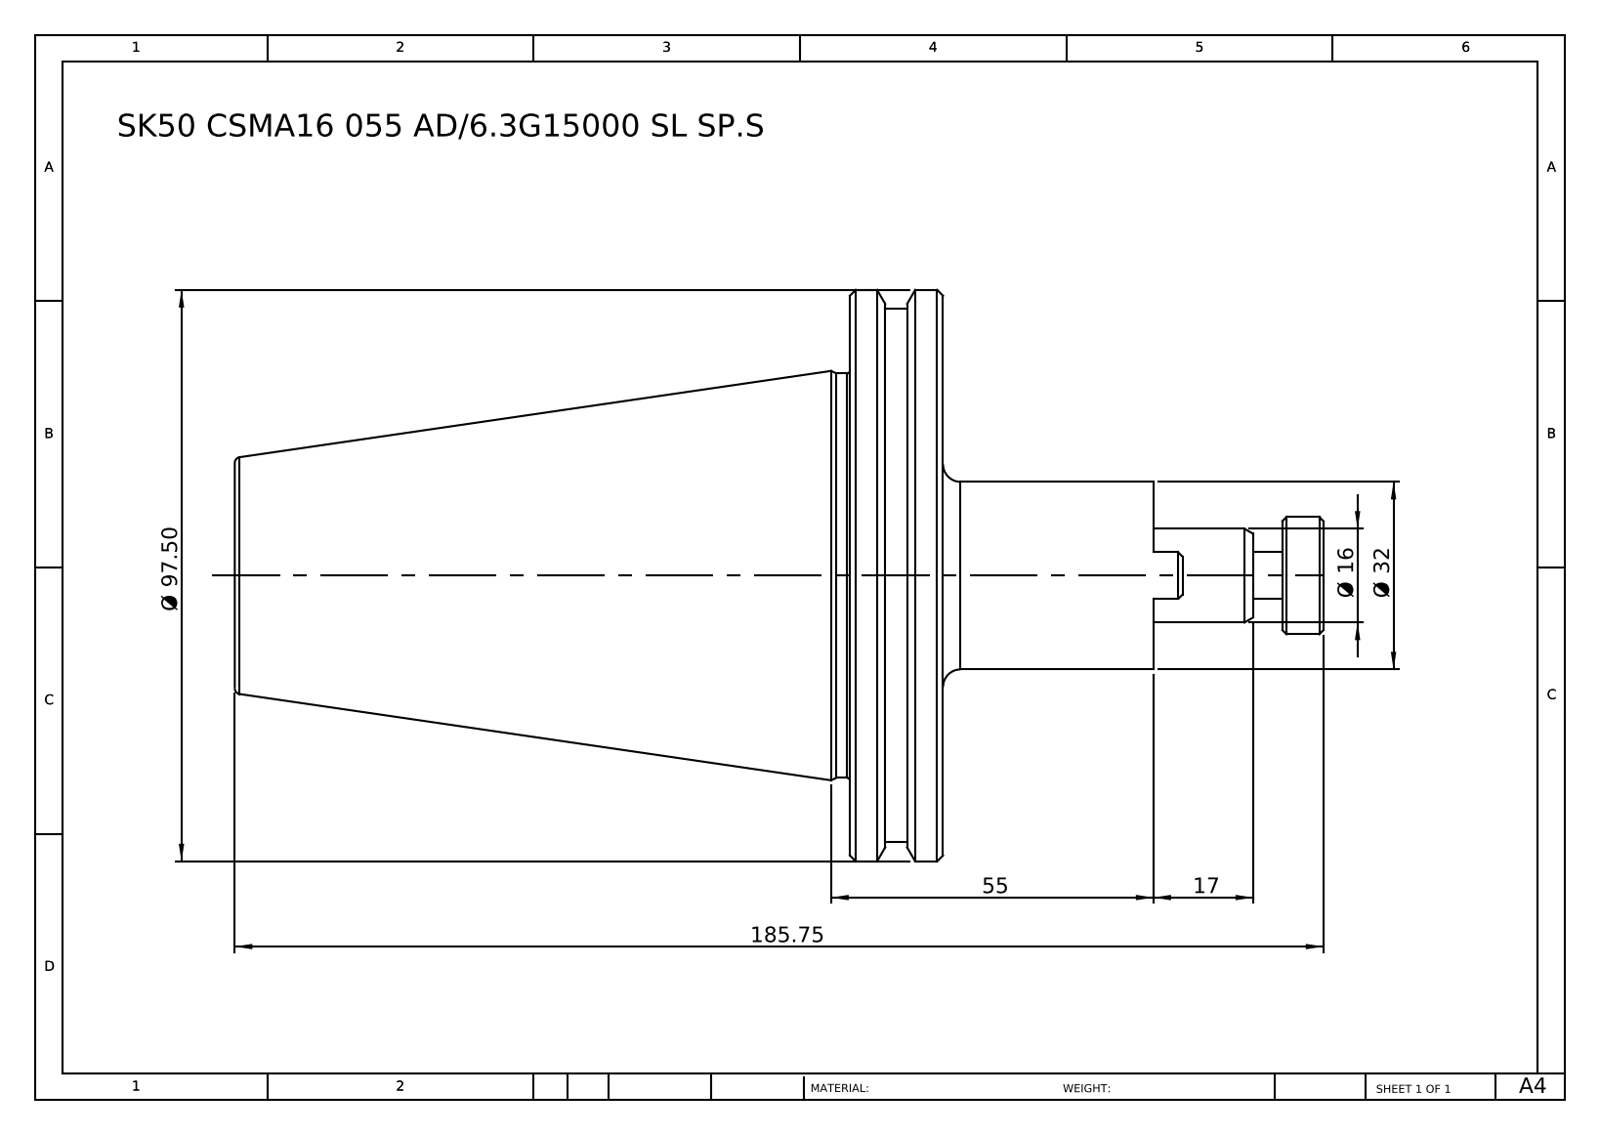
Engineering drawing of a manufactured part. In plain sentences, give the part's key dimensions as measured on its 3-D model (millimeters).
The part is named "SK 50 CSMA16 055 AD-6.3G15000 SL SP.S". Its 3-D file was written by "SolidWorks 2014 (CONFIG_CONTROL_DESIGN)". It is 1 solid with 62 faces: 20 planar, 16 cylindrical and 26 other. Overall it measures 185.75 by 97.5 by 97.5 millimeters. Its volume is 409 041 cubic millimeters and its surface area 42 087 square millimeters. Round bosses or shafts: 1 of diameter 97.5, 1 of diameter 91, 1 of diameter 69, 1 of diameter 32, 1 of diameter 20, 1 of diameter 16, 1 of diameter 8. The main face-to-face distances are 15.9, 120.85, 104.95, 35.9, 51.8, 156.75, 29, 64.9, 80.8, 185.75.
